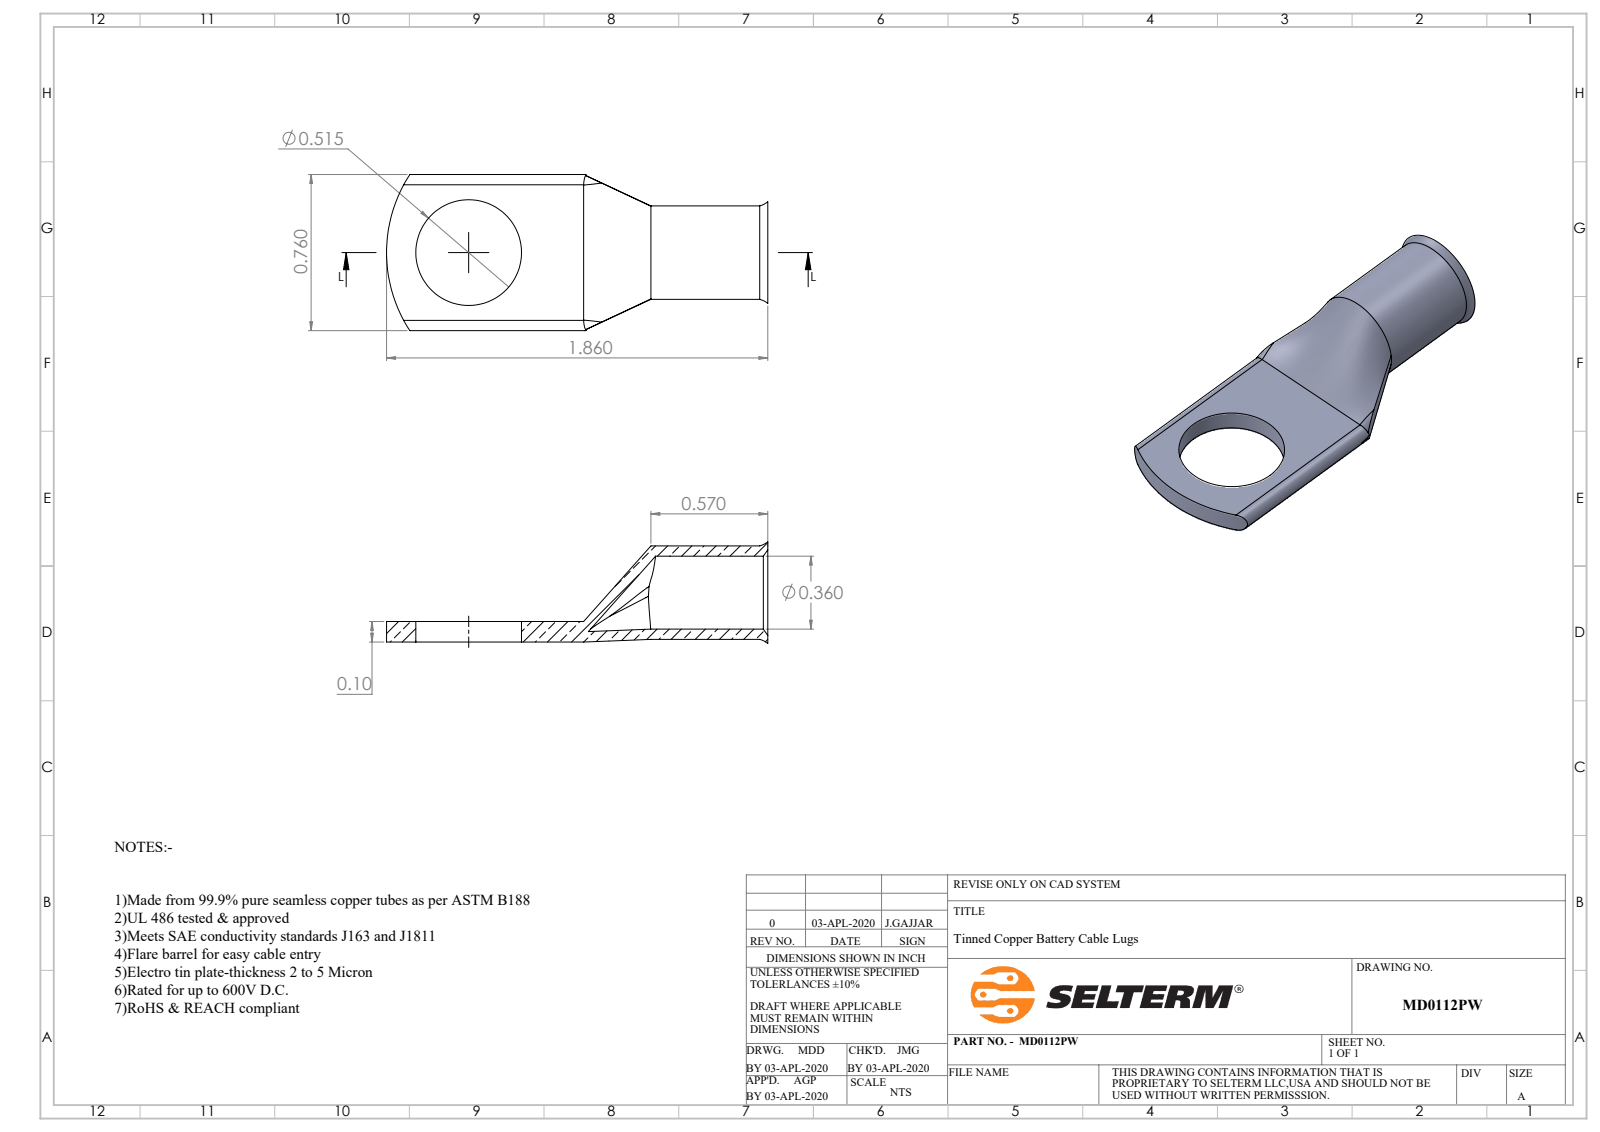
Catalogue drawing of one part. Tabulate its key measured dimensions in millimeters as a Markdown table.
| quantity | value |
| --- | --- |
| part name | MD0112PW(1) |
| STEP written by | SolidWorks 2021 (AUTOMOTIVE_DESIGN) |
| units | millimeters |
| bodies | 1 solid, 31 faces (3 planar, 10 cylindrical, 18 other) |
| overall size | 47.18 × 19.3 × 12.56 |
| volume | 1 781 mm³ |
| surface area | 2 458 mm² |
| round holes (diameter × count) | 9.02 × 1, 13.08 × 1 |
| round bosses / shafts (diameter × count) | 11.56 × 1 |
| partial cylindrical surfaces (radius × count) | 1.27 × 2, 17.62 × 1 |
| main face-to-face distances | 2.54 |
